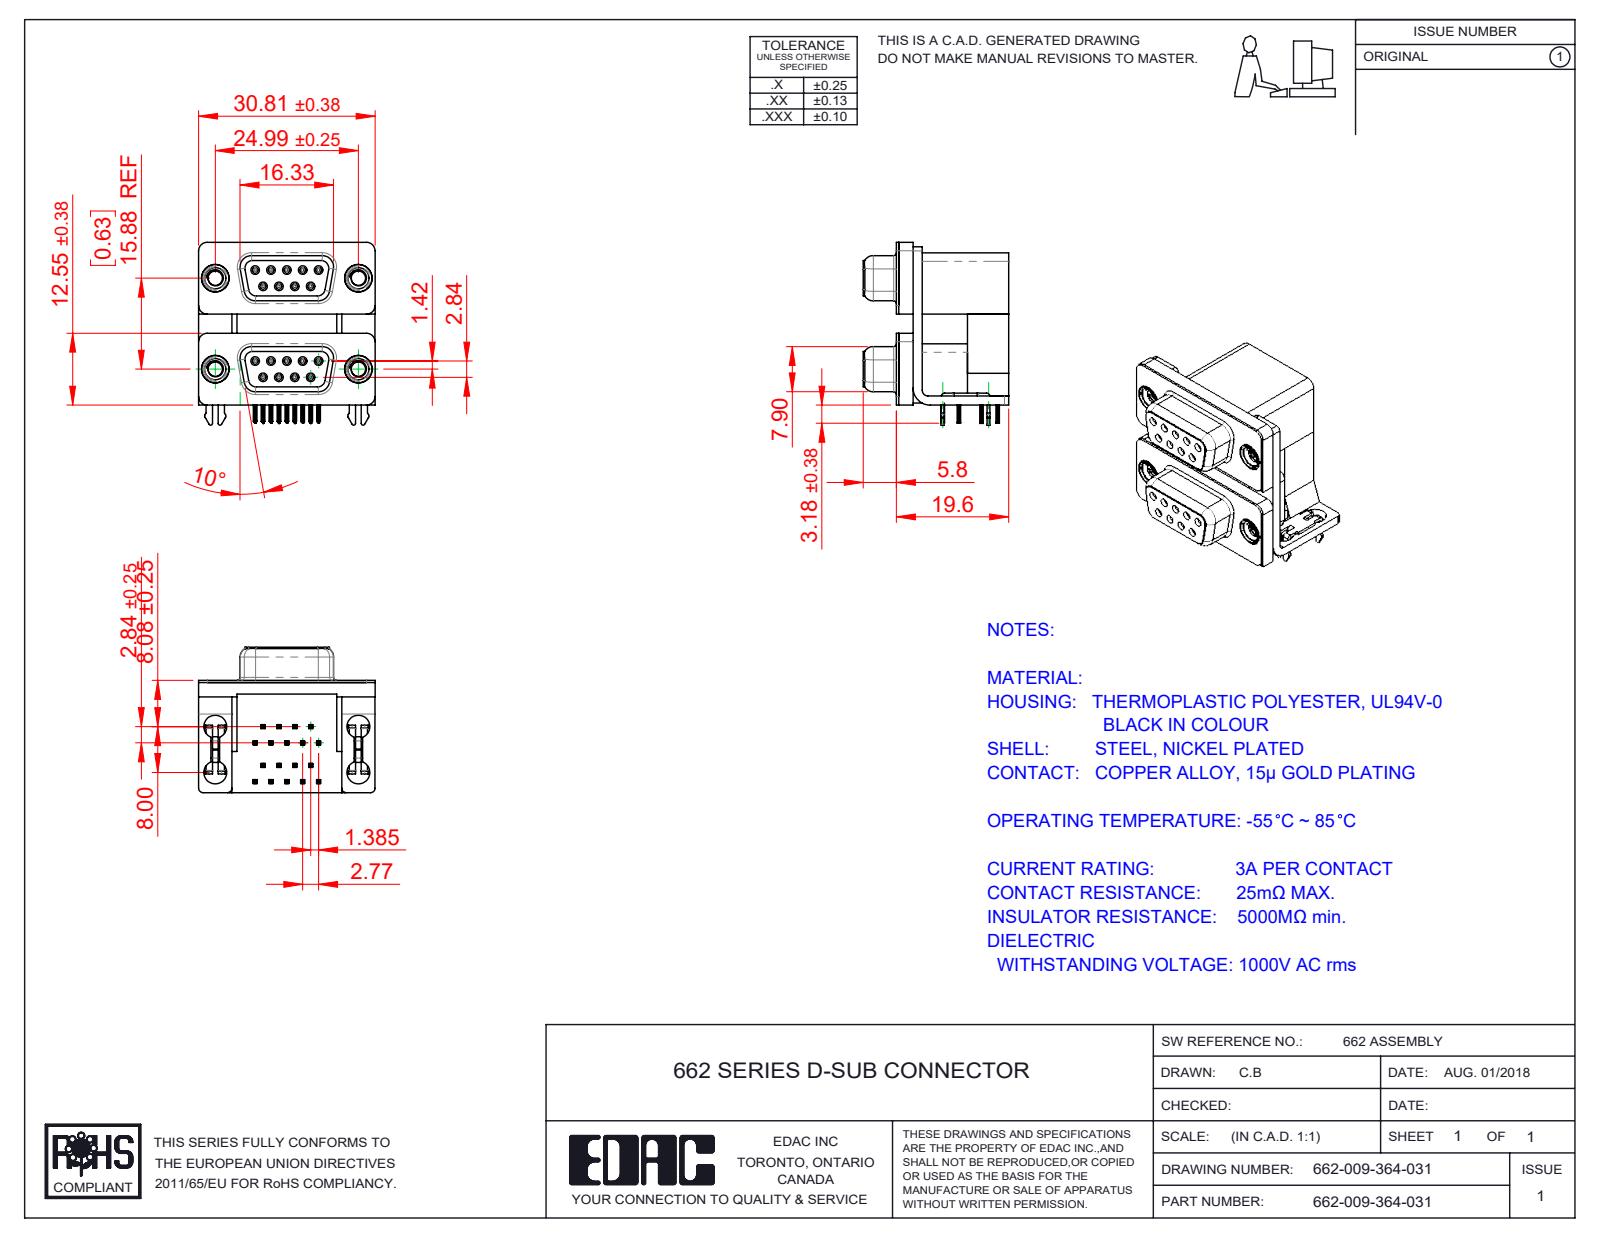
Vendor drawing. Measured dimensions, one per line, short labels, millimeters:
name: 662 Housing Spacer_09 Contacts L; 662 Housing Lower_09 Contacts; 662 Contact Top Lower; 662 Contact Top Upper_L (+8 more)
written by: SolidWorks 2020 (CONFIG_CONTROL_DESIGN)
unit: mm
bodies: 31 solids, 3266 faces (1476 planar, 854 cylindrical, 936 other)
size: 31.93 × 30.81 × 25.4
volume: 10 844 mm³; area: 13 050 mm²
holes: 18× ⌀0.8, 18× ⌀0.9, 8× ⌀4, 4× ⌀2.5, 4× ⌀3.5, 4× ⌀4.8, 4× ⌀5
bosses: 18× ⌀1.2, 4× ⌀4.9, 4× ⌀4.75, 4× ⌀3.9
rounds: 146× R0.1, 72× R0.15, 36× R0.35, 18× R0.34, 18× R1.35, 12× R0.5, 12× R1.5, 10× R0.25
face distances: 2.5, 0.4, 16.7, 19.2, 2.9, 19.6, 15.88, 7.2, 9.5, 12
hole spacings: 3.16, 2.77, 16.12, 15.88, 5.54, 16.82, 13.11, 18.77
